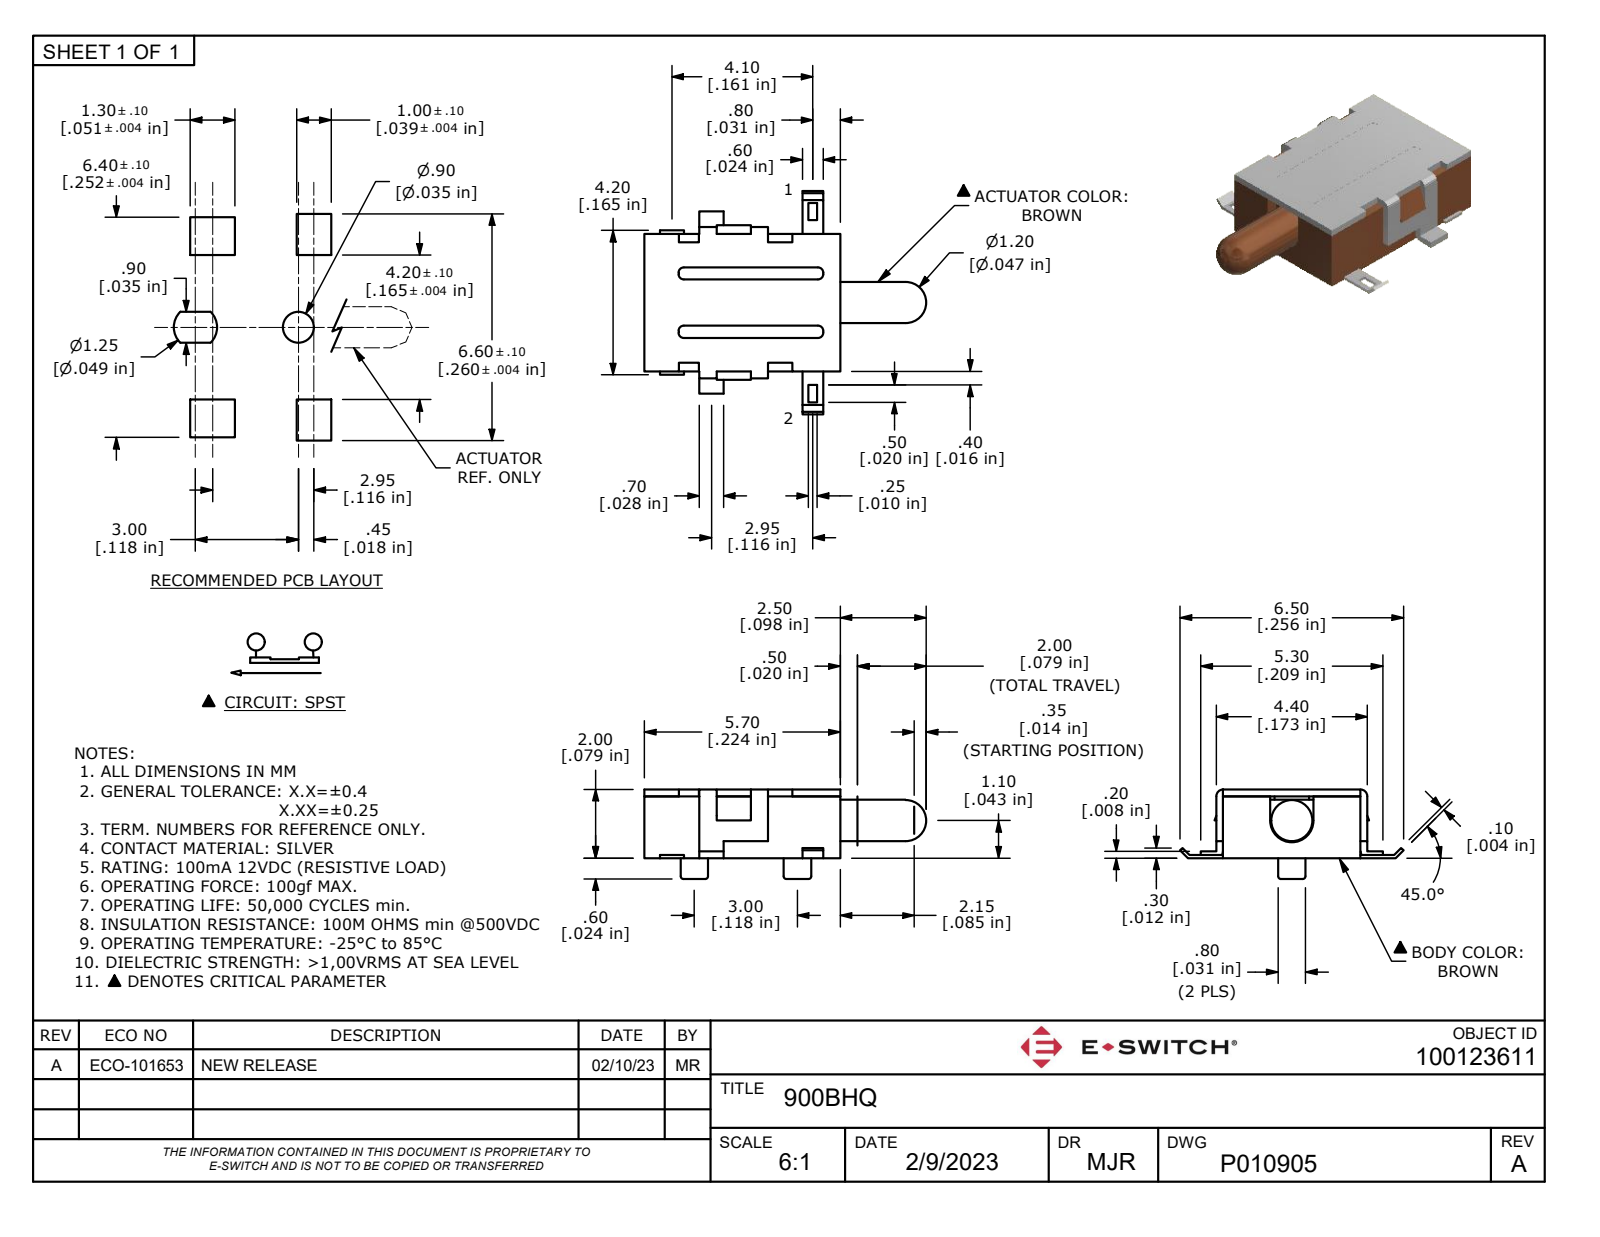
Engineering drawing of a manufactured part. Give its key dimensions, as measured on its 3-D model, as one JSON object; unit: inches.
{"part_name": "900BHQ", "step_written_by": "Autodesk Inventor 2022 (AUTOMOTIVE_DESIGN)", "units": "inches", "bodies": {"solids": 1, "faces": 162, "planar": 133, "cylindrical": 22, "other": 7}, "overall_size": [0.323, 0.256, 0.102], "volume_in3": 0.002, "surface_area_in2": 0.29, "round_holes": [[0.01, 4]], "round_bosses_or_shafts": [[0.031, 2], [0.047, 1]], "partial_cylinders_radius": [[0.006, 8], [0.008, 4], [0.024, 1]], "face_to_face_distances": [0.079, 0.059, 0.067, 0.014, 0.071, 0.051, 0.055, 0.144, 0.063, 0.02], "hole_center_spacings": [0.079, 0.138, 0.159]}
